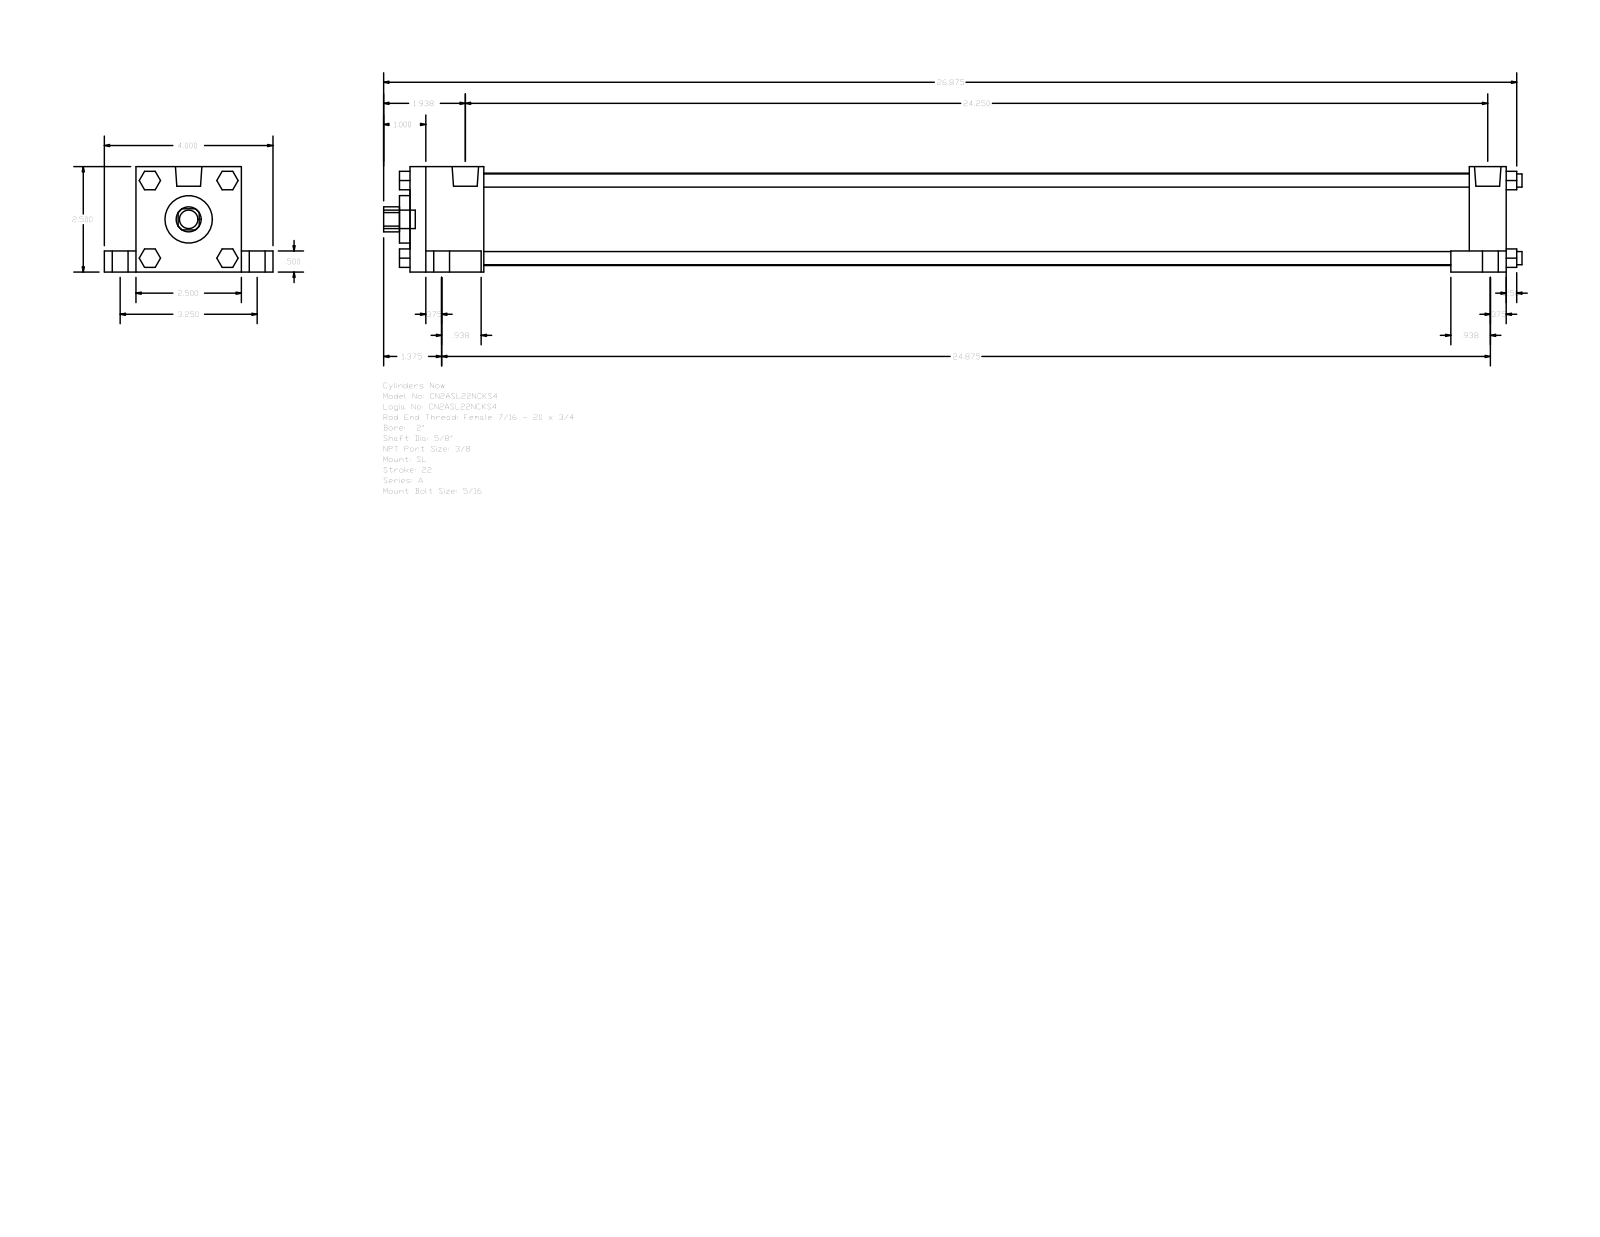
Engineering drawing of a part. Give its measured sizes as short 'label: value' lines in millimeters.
name: A_SL__0200_0.625
written by: GSSL Pune (CONFIG_CONTROL_DESIGN)
unit: mm
bodies: 0 solids, 148 faces (112 planar, 36 cylindrical, 0 other)
size: 685.8 × 101.6 × 63.5
holes: 1× ⌀15.88, 1× ⌀28.57, 1× ⌀55.63
bosses: 4× ⌀15.88, 4× ⌀9.53, 4× ⌀7.94, 4× ⌀5.56, 2× ⌀15.93, 1× ⌀11.11
rounds: 1× R7.54
face distances: 63.5, 660.39, 50.8, 12.7, 19.05, 82.55, 44.45, 615.94, 638.17, 593.72
